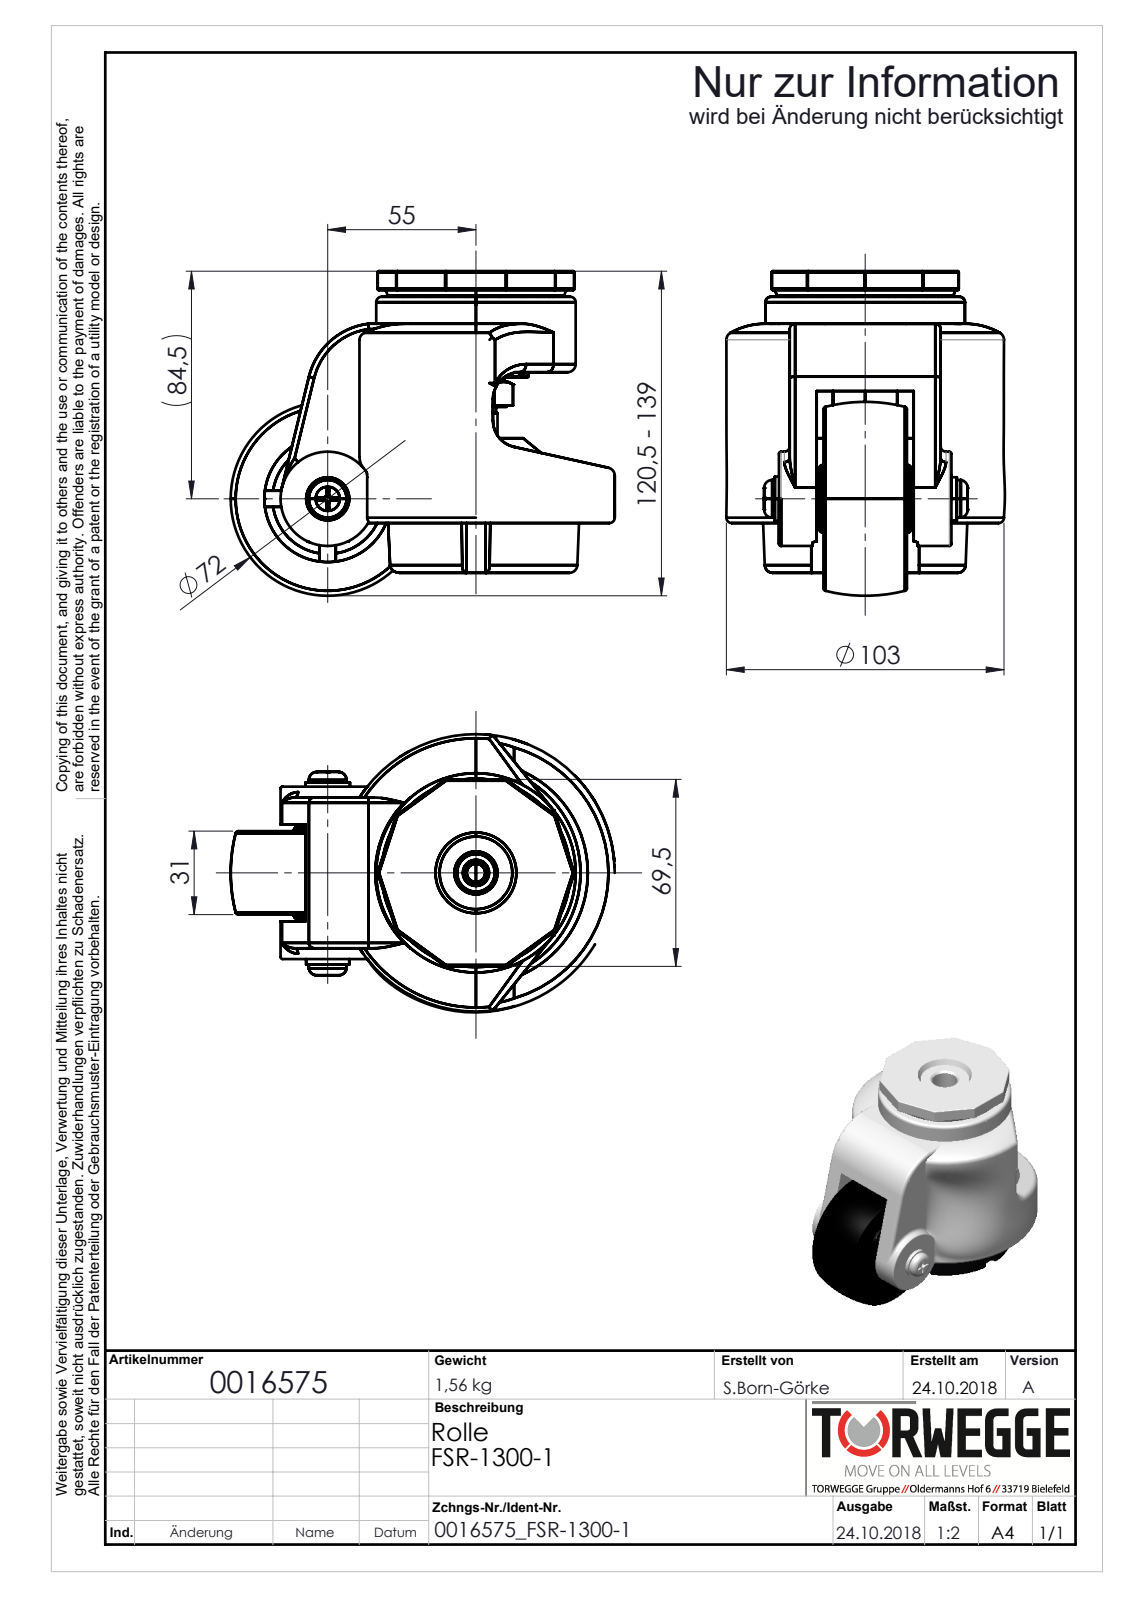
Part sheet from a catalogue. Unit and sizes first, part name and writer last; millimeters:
Units: millimetres
Overall size (bounding box): 142.51 × 120.46 × 109.82
Round bosses / shafts (diameter × count): ⌀16 ×2, ⌀14 ×2, ⌀6.8 ×2, ⌀74 ×1, ⌀47 ×1, ⌀41.4 ×1, ⌀41.2 ×1, ⌀40 ×1
Partial cylindrical surfaces — rounded edges, fillets, slot ends (radius × count): R0.5 ×30, R5 ×20, R8 ×8, R3 ×6, R2 ×4, R10 ×2, R7.5 ×1, R13.74 ×1
Main face-to-face distances: 35.5, 50, 37.5, 2.5, 24.5, 56, 8, 12.5, 53, 33.5
Bodies: 0 solids, 668 faces (209 planar, 189 cylindrical, 270 other)
Part name (STEP PRODUCT): K0016575_FSR-1300-1_FSR-1300-1
STEP written by: SolidWorks 2018 (AUTOMOTIVE_DESIGN)
